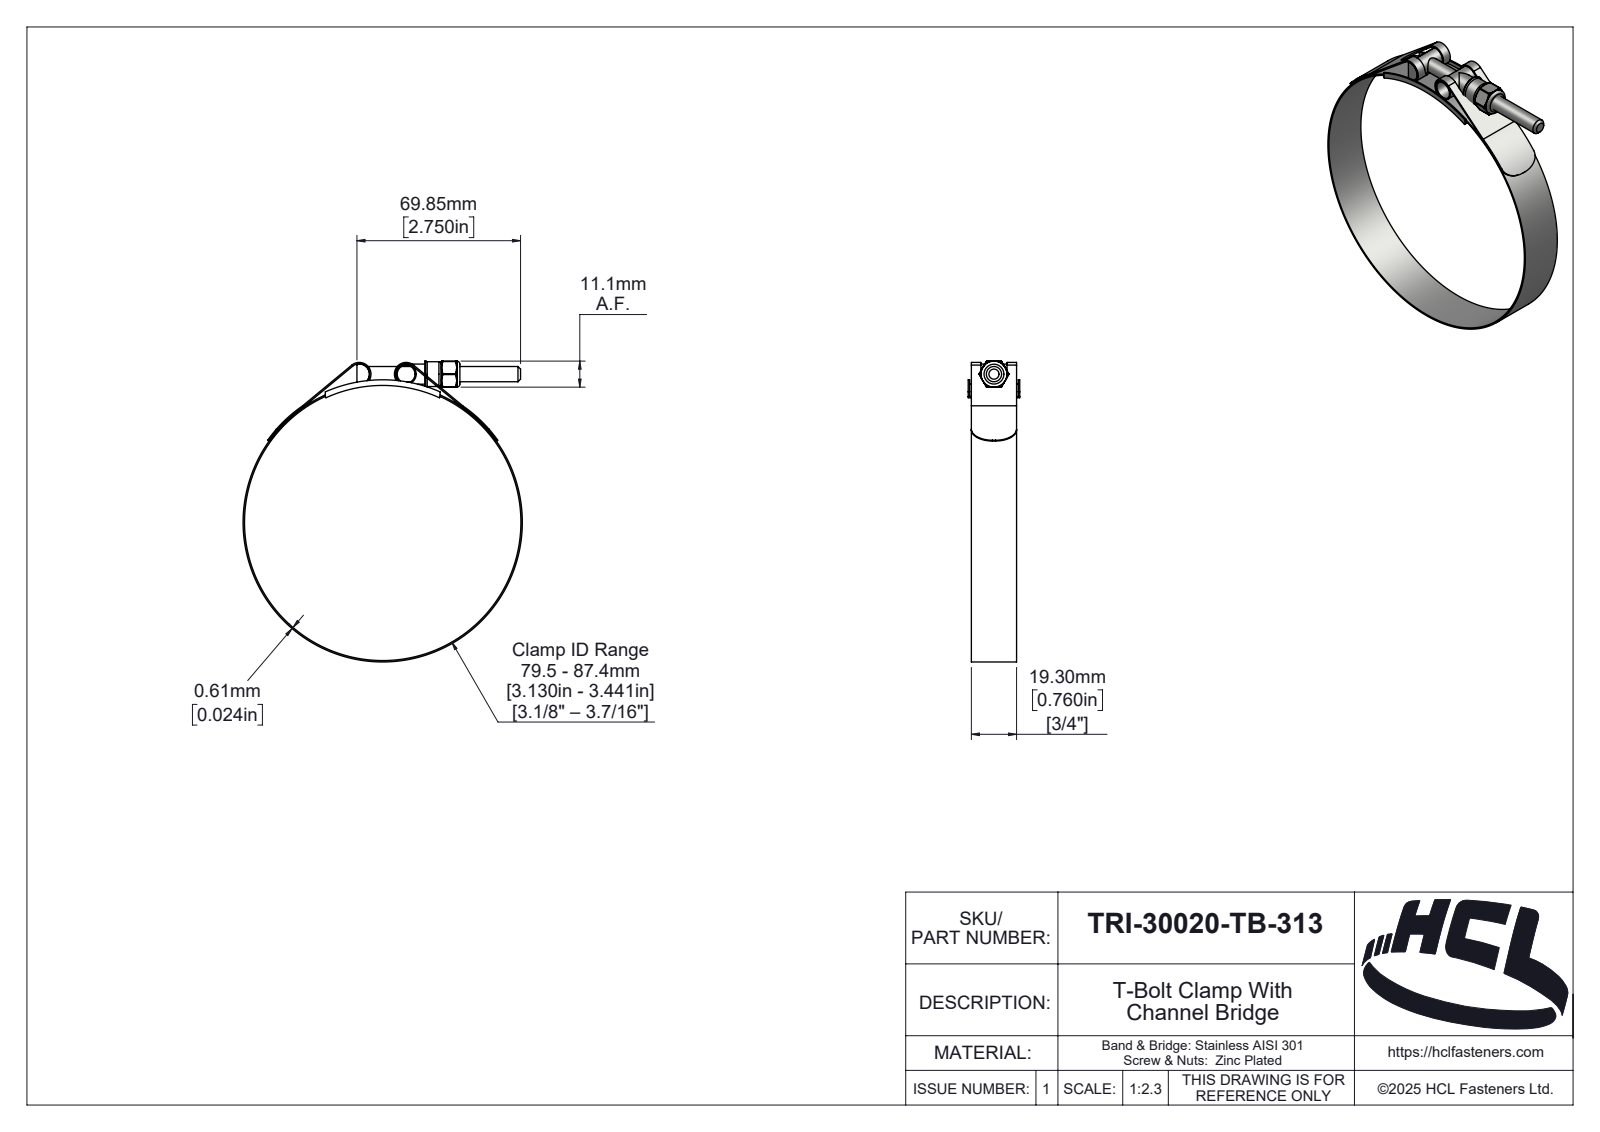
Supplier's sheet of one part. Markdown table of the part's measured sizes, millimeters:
| quantity | value |
| --- | --- |
| part name | TRI-30020-TB-313 |
| STEP written by | SolidWorks 2025 (AUTOMOTIVE_DESIGN) |
| units | millimeters |
| bodies | 6 solids, 330 faces (44 planar, 122 cylindrical, 164 other) |
| overall size | 128.54 × 119.22 × 22 |
| volume | 10 294 mm³ |
| surface area | 25 149 mm² |
| round holes (diameter × count) | 5.4 × 1, 6.35 × 1, 6.5 × 1, 7.58 × 1, 118 × 1 |
| round bosses / shafts (diameter × count) | 8.58 × 2, 119.22 × 1, 10.58 × 1 |
| partial cylindrical surfaces (radius × count) | 0.39 × 6, 0.5 × 2, 4.39 × 2, 5 × 2, 0.59 × 1, 2.42 × 1, 3.03 × 1, 3.19 × 1 |
| main face-to-face distances | 0.61, 19.3, 1.35, 20.65, 0.74, 21.39, 20.04, 22, 11.11, 20.78 |
| hole center spacings | 64 |
